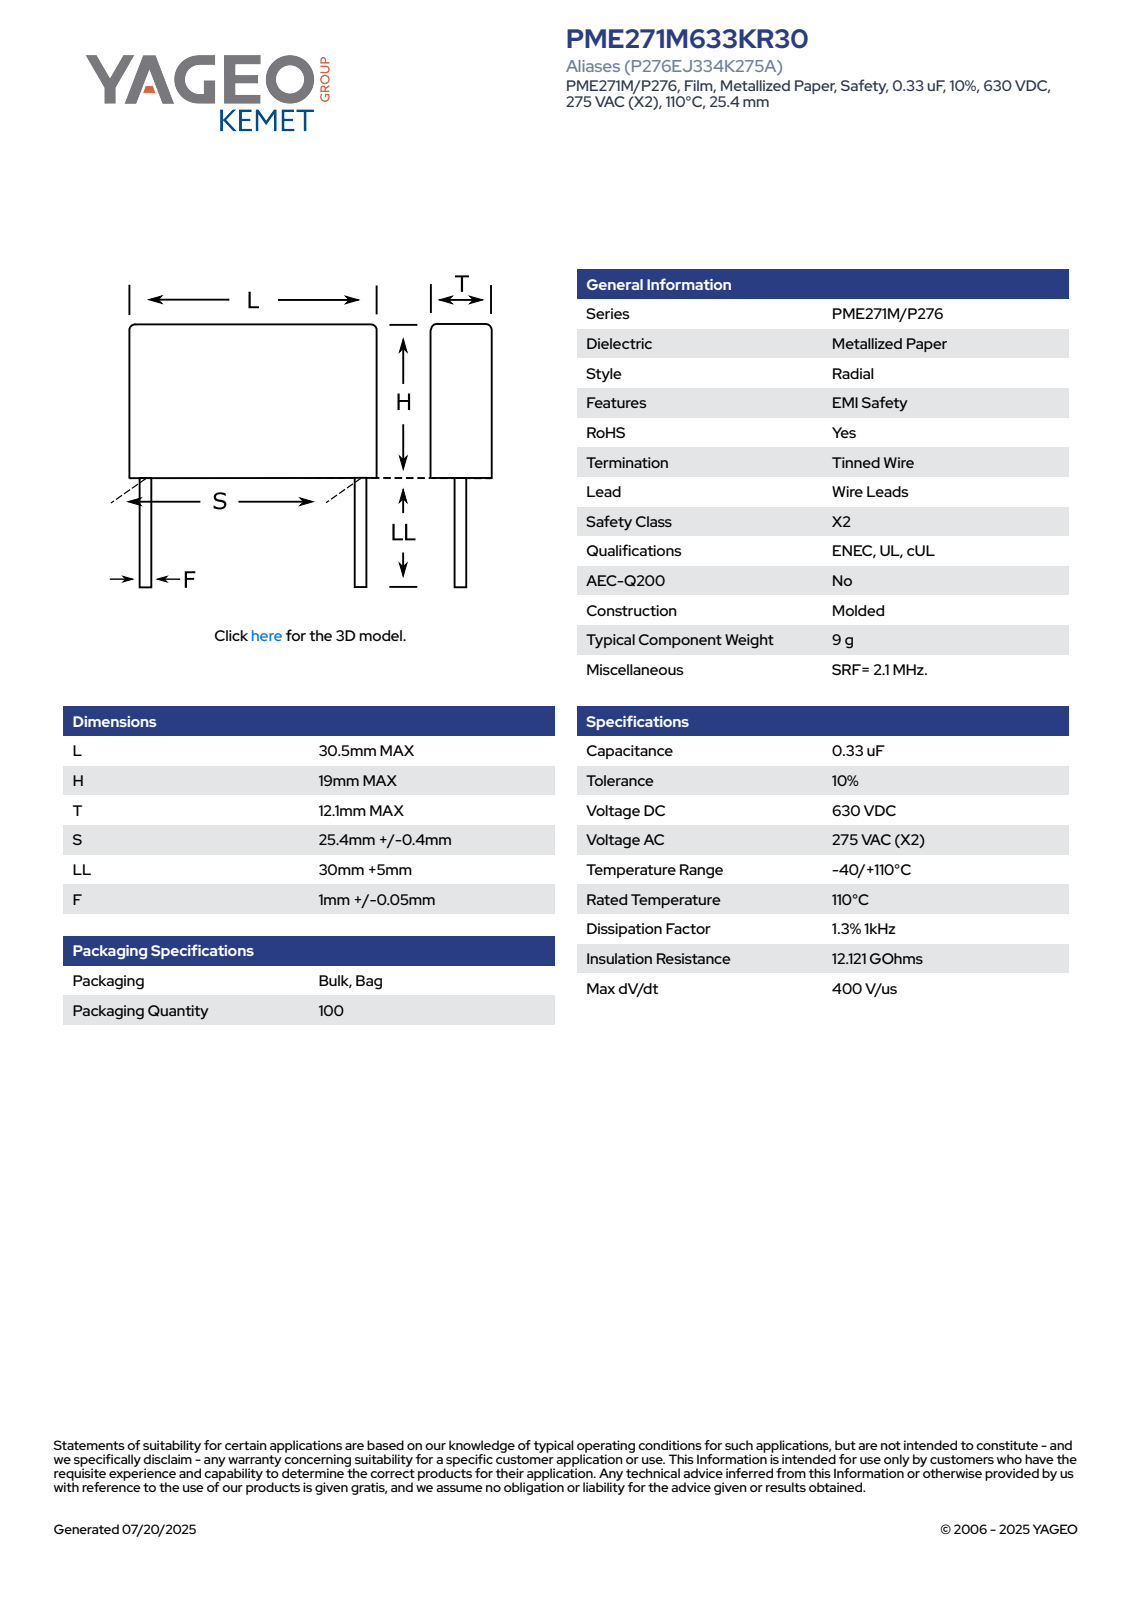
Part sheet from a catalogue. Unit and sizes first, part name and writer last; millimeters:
Units: millimetres
Overall size (bounding box): 54 × 30.5 × 12.11
Round bosses / shafts (diameter × count): ⌀1 ×2
Partial cylindrical surfaces — rounded edges, fillets, slot ends (radius × count): R0.5 ×4
Main face-to-face distances: 12.1, 19, 30.5, 35, 54, 45.7, 10.7, 8.3, 42.97, 7.97
Volume: 7 063 mm³ · Surface area: 2 603 mm²
Bodies: 4 solids, 73 faces (65 planar, 8 cylindrical, 0 other)
Part name (STEP PRODUCT): CFR_MOLDED_30.5X19X12.1_L30.5H19T12.1S25.4LL35F1
STEP written by: SolidWorks 2014 (AUTOMOTIVE_DESIGN)
